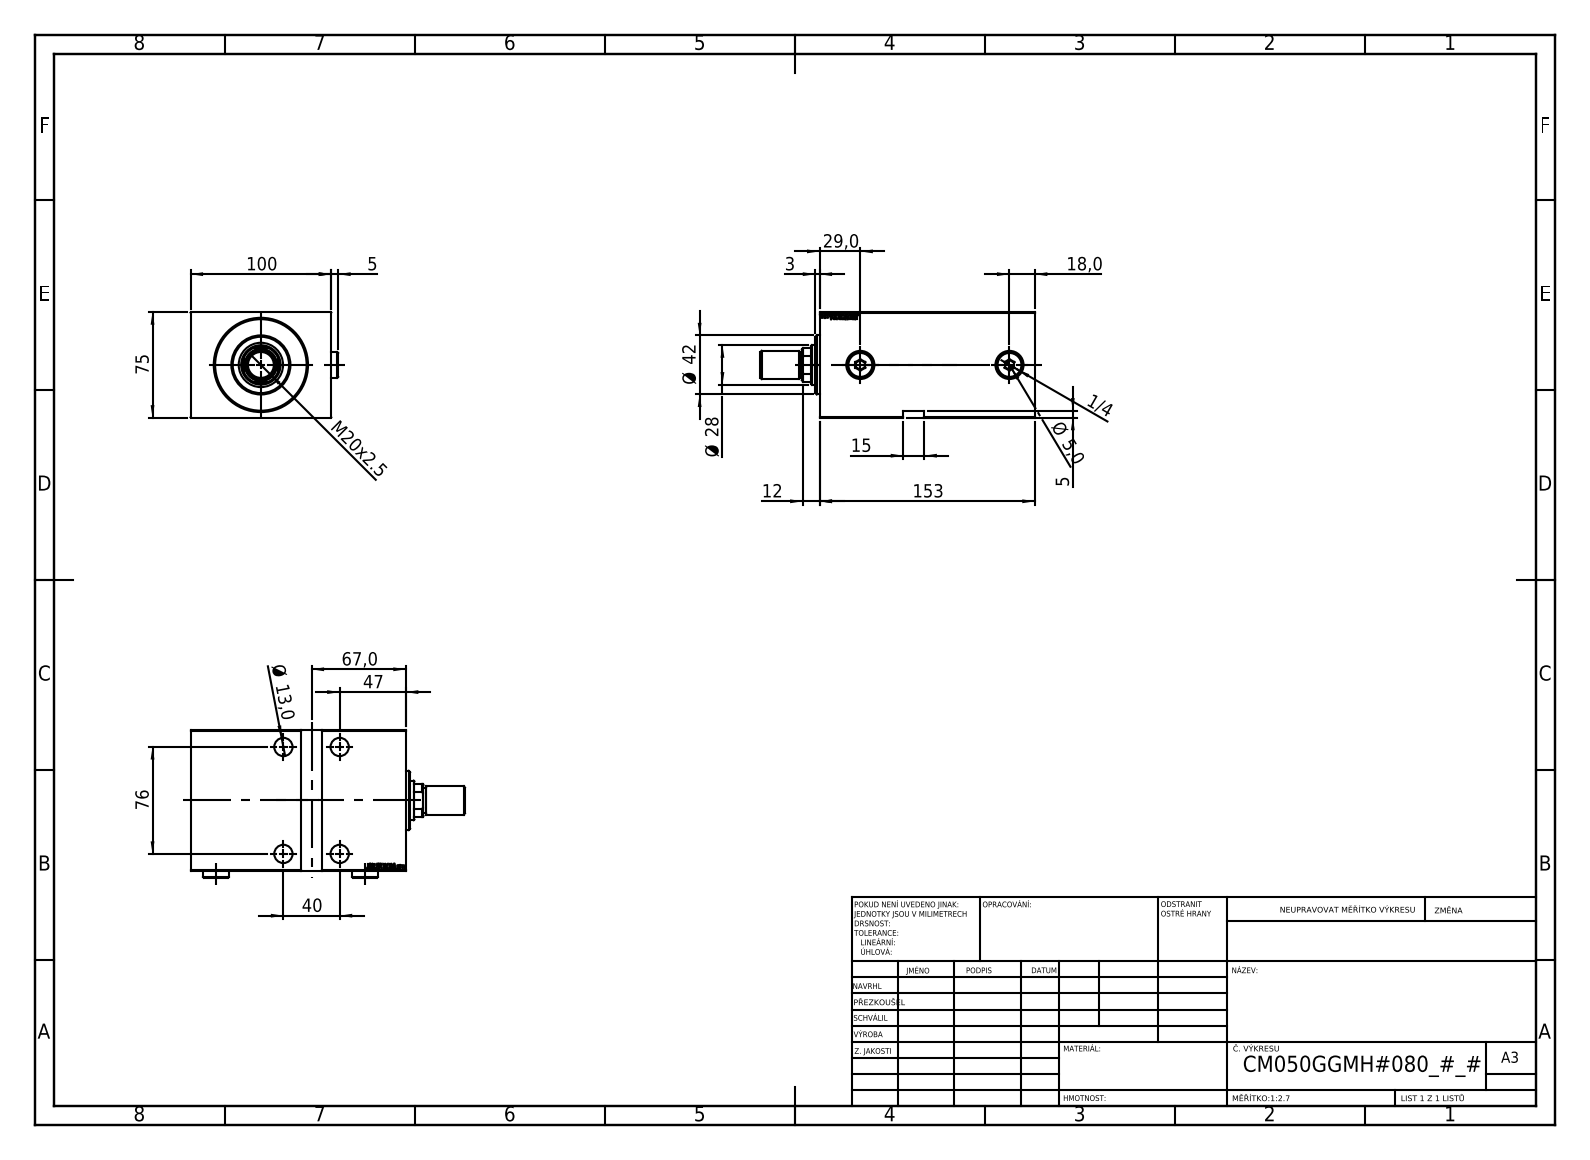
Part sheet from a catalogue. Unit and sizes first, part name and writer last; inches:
Units: inches
Overall size (bounding box): 7.677 × 4.13 × 2.953
Round holes (diameter × count): ⌀0.512 ×4, ⌀0.748 ×4, ⌀0.197 ×2, ⌀0.518 ×2, ⌀0.787 ×2, ⌀0.728 ×1, ⌀1.102 ×1, ⌀1.24 ×1, ⌀1.969 ×1, ⌀2.047 ×1, ⌀2.559 ×1
Round bosses / shafts (diameter × count): ⌀0.709 ×3, ⌀1.654 ×1, ⌀0.787 ×1
Partial cylindrical surfaces — rounded edges, fillets, slot ends (radius × count): R0.531 ×1
Main face-to-face distances: 2.953, 3.937, 6.024, 0.197, 5.276, 0.551, 5.472, 5.827, 3.425, 1.85
Hole centre spacings: 1.575, 2.992, 3.381, 4.173
Volume: 59.68 in³ · Surface area: 216 in²
Bodies: 6 solids, 910 faces (446 planar, 60 cylindrical, 404 other)
Part name (STEP PRODUCT): V450CM_VC_G; V450CM_G_VCP; V450CM_G_Body; V450CM_MALE_METRIC (+1 more)
STEP written by: SolidWorks 2019 (CONFIG_CONTROL_DESIGN)
